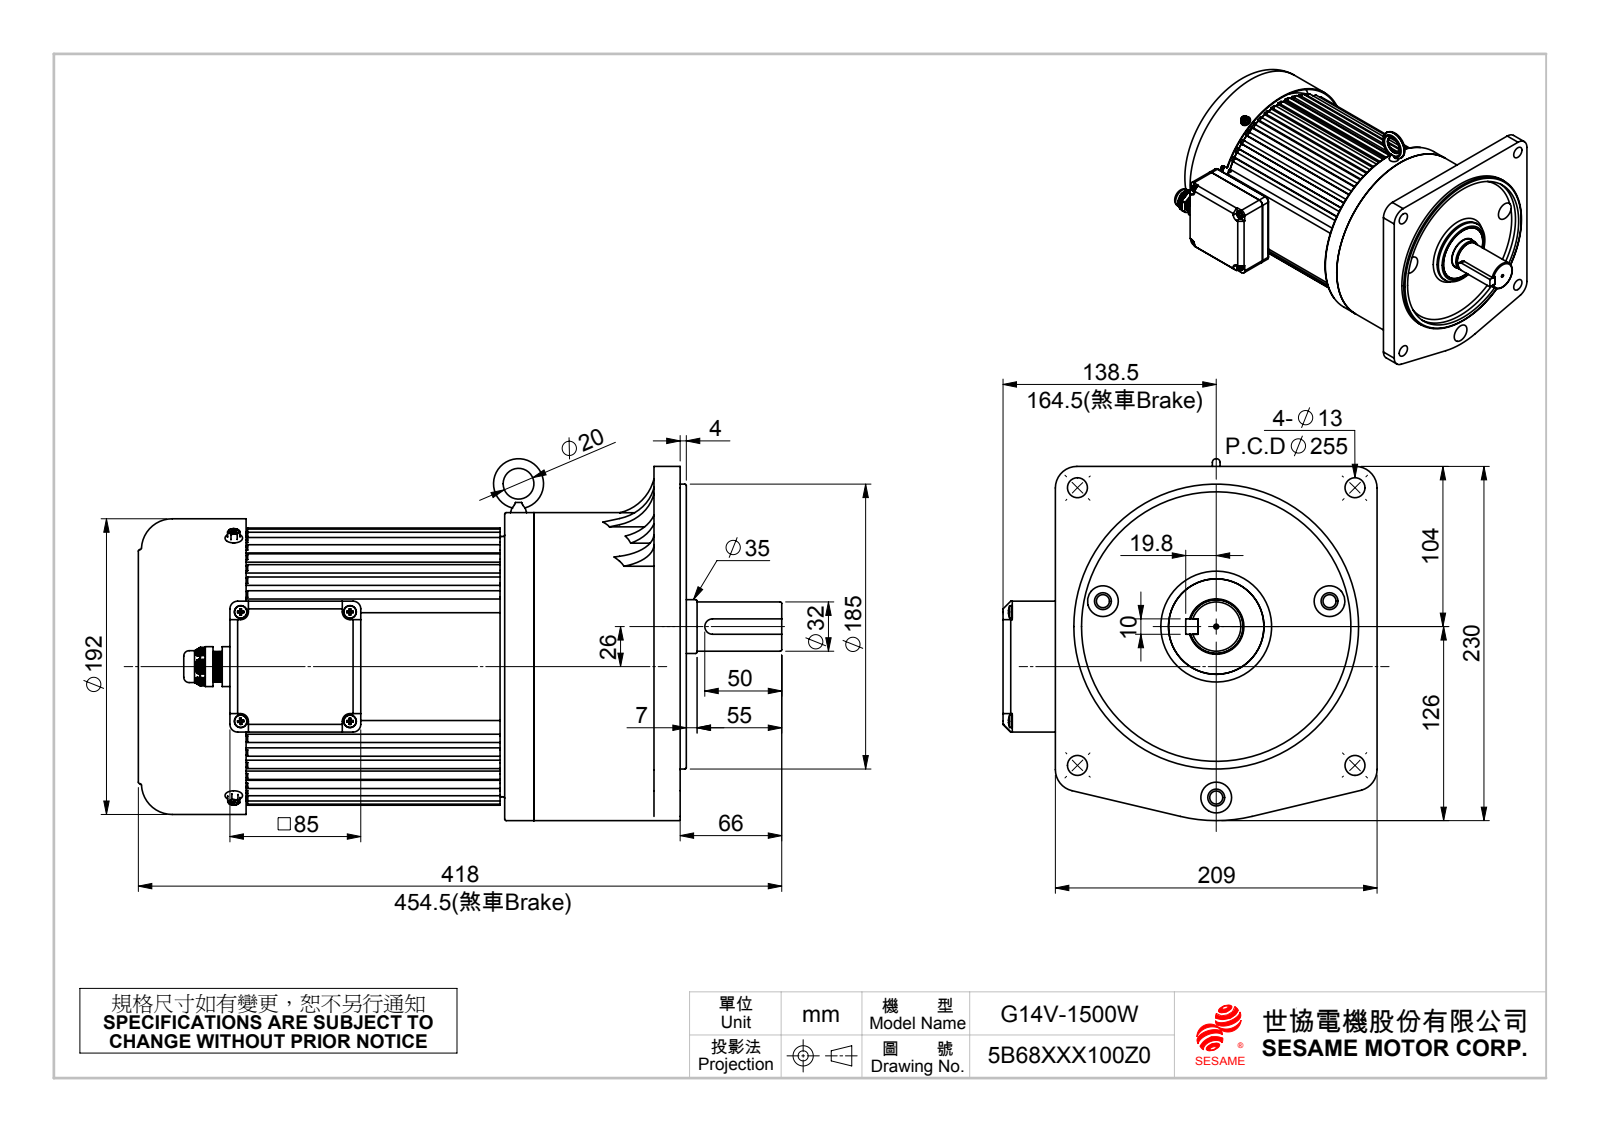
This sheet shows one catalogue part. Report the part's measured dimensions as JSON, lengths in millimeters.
{"part_name": "出線盒上蓋; 出線盒墊片JTH-UP3(PVC2mm厚); 油封35x62x8; G140S1 (+8 more)", "step_written_by": "SolidWorks 2010 (CONFIG_CONTROL_DESIGN)", "units": "millimeters", "bodies": {"solids": 20, "faces": 3192, "planar": 1206, "cylindrical": 915, "other": 1071}, "overall_size": [418, 243, 235], "volume_mm3": 8525000, "surface_area_mm2": 722828, "round_holes": [[5, 11], [3.3, 9], [6, 4], [8, 4], [13, 4], [20, 4], [4.2, 3], [11, 3], [15, 3], [2, 1], [6.5, 1], [6.8, 1]], "round_bosses_or_shafts": [[8.3, 4], [4, 4], [5, 3], [200, 1], [192, 1], [190, 1], [185, 1], [171, 1]], "partial_cylinders_radius": [[2.25, 42], [0.5, 24], [1, 24], [3, 20], [5, 9], [30, 7], [2.9, 6], [14, 6]], "face_to_face_distances": [195, 2, 4, 27, 168, 9.5, 177.5, 204.5, 175.5, 166], "hole_center_spacings": [45, 58.25, 71, 82.38, 127.51, 147.22, 180.32, 75.5]}
